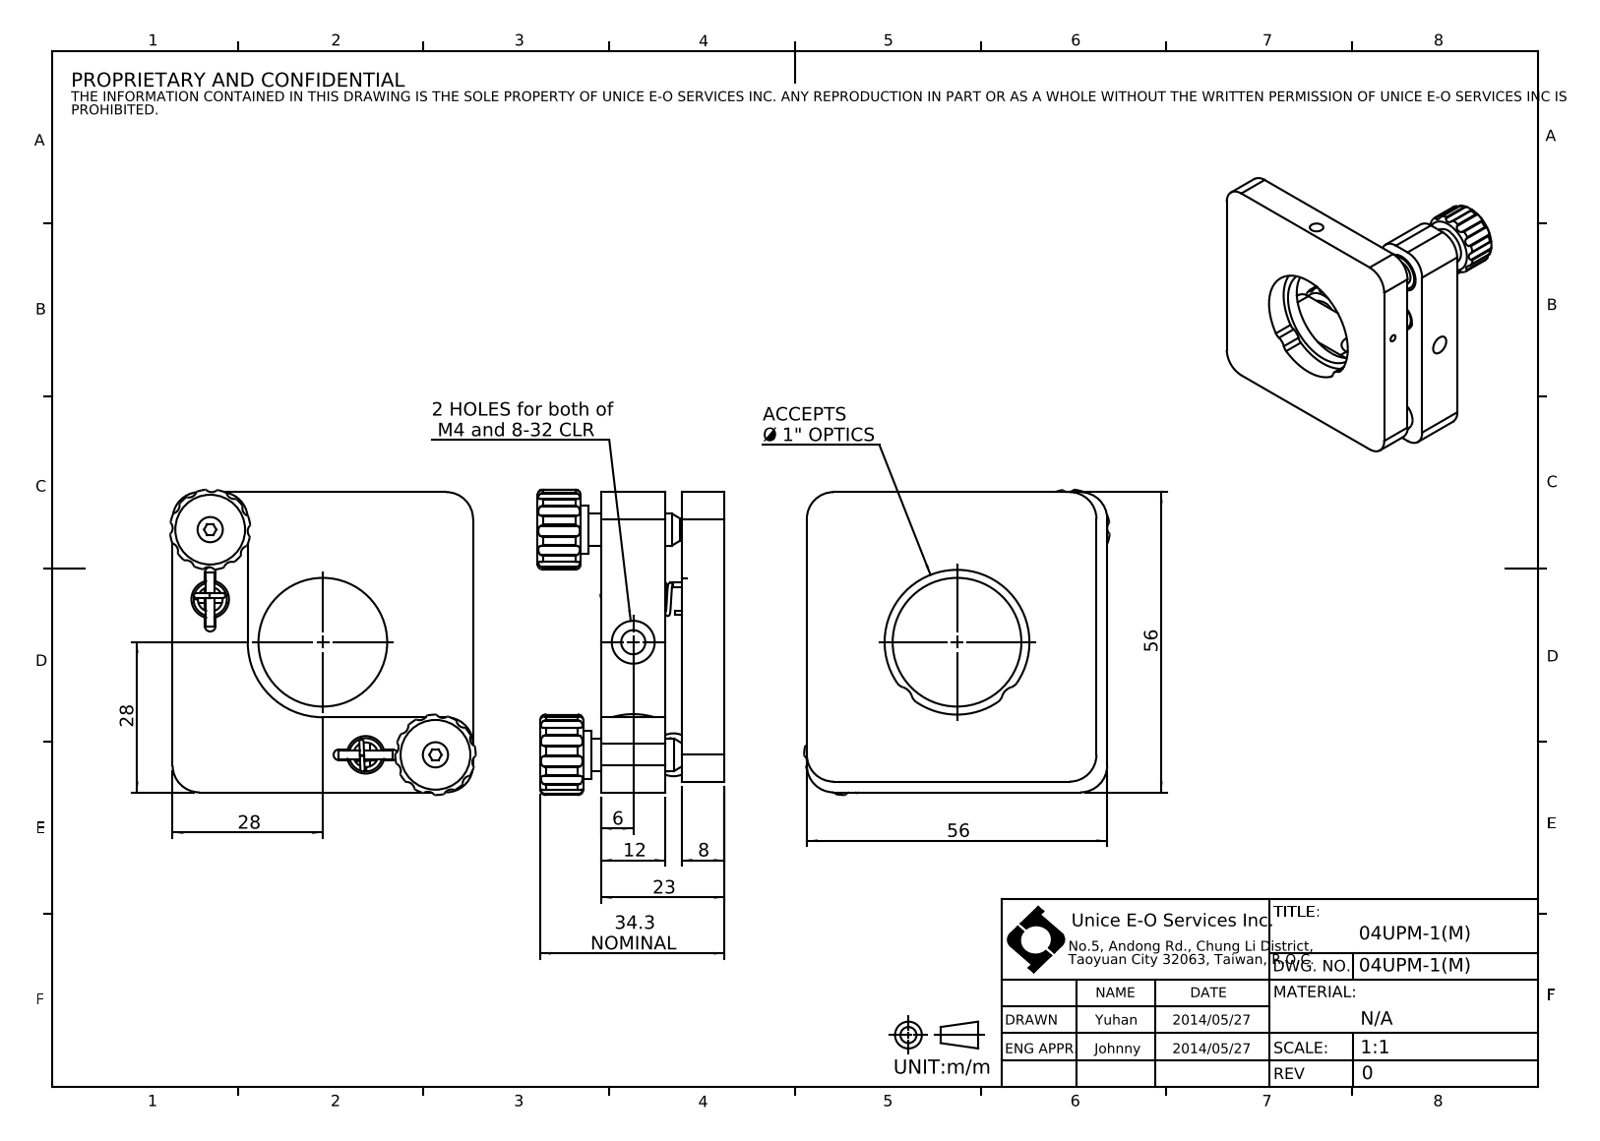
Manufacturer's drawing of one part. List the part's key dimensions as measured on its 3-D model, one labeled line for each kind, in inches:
Part name (STEP PRODUCT): 04UPM-1(M)
STEP written by: SolidWorks 2016 (CONFIG_CONTROL_DESIGN)
Units: inches
Bodies: 21 solids, 413 faces (111 planar, 238 cylindrical, 64 other)
Overall size (bounding box): 2.243 × 2.243 × 1.391
Volume: 2.217 in³ · Surface area: 31.36 in²
Round holes (diameter × count): ⌀0.047 ×4, ⌀0.067 ×2, ⌀0.157 ×2, ⌀0.177 ×2, ⌀0.185 ×2, ⌀0.232 ×2, ⌀0.236 ×2, ⌀0.276 ×2, ⌀0.315 ×2, ⌀0.374 ×2, ⌀0.13 ×1, ⌀0.25 ×1
Round bosses / shafts (diameter × count): ⌀0.031 ×16, ⌀0.063 ×4, ⌀0.354 ×2, ⌀0.248 ×1, ⌀0.157 ×1, ⌀0.098 ×1
Partial cylindrical surfaces — rounded edges, fillets, slot ends (radius × count): R0.012 ×48, R0.059 ×24, R0.197 ×9, R0.039 ×4, R0.079 ×4, R0.098 ×2, R0.295 ×2, R0.551 ×1
Main face-to-face distances: 0.315, 0.472, 0.118, 0.433, 0.906, 0.591, 2.205, 0.079, 2.126, 1.654
Hole centre spacings: 0.512, 0.635, 0.844, 0.885, 1.169, 1.35, 2.009, 0.315
